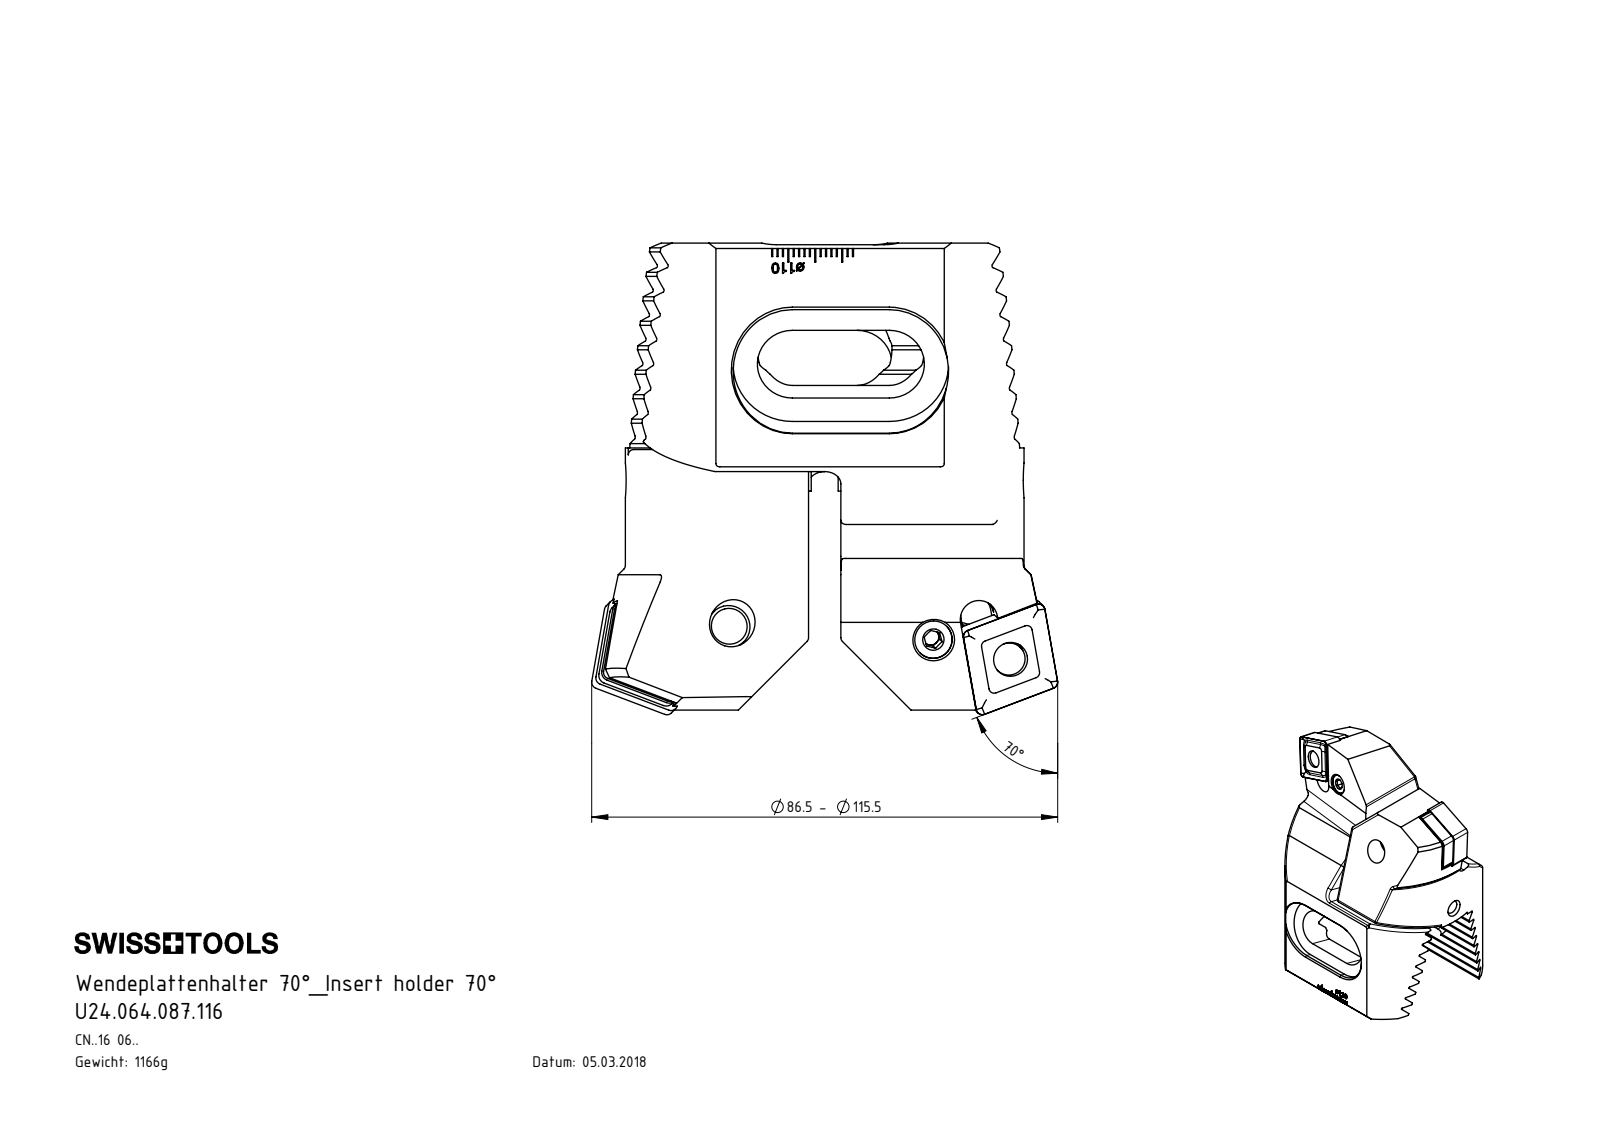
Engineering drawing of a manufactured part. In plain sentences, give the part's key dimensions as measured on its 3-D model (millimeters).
The part is named "Z72.WCE.B70.050; WCE-ER4.101.020_A; WCE-ER2.101.004_A; Z72-xxx.001.050_C_CN 16 70ø (+5 more)". Its 3-D file was written by "SolidWorks 2017 (AUTOMOTIVE_DESIGN)". It is 14 solids with 806 faces: 486 planar, 128 cylindrical and 192 other. Overall it measures 87.5 by 86.5 by 58.2 millimeters. Its volume is 148 468 cubic millimeters and its surface area 43 791 square millimeters. Round holes: 2 of diameter 2, 2 of diameter 6.35, 2 of diameter 7, 2 of diameter 8.05, 2 of diameter 8.4, 1 of diameter 5. Round bosses or shafts: 3 of diameter 6, 2 of diameter 8, 2 of diameter 7.9, 2 of diameter 6.4, 2 of diameter 3.55, 1 of diameter 4. Partial cylindrical surfaces (rounded edges, fillets, slot ends): 16 of radius 0.34, 16 of radius 1, 8 of radius 1.2, 8 of radius 1.5, 6 of radius 3, 6 of radius 3.5, 4 of radius 0.3, 4 of radius 6.5. The main face-to-face distances are 4.07, 8.14, 20.36, 12.21, 16.29, 20.34, 24.43, 6, 1.61, 58.2. The hole center spacings are 14.78, 15, 20, 38.64.
